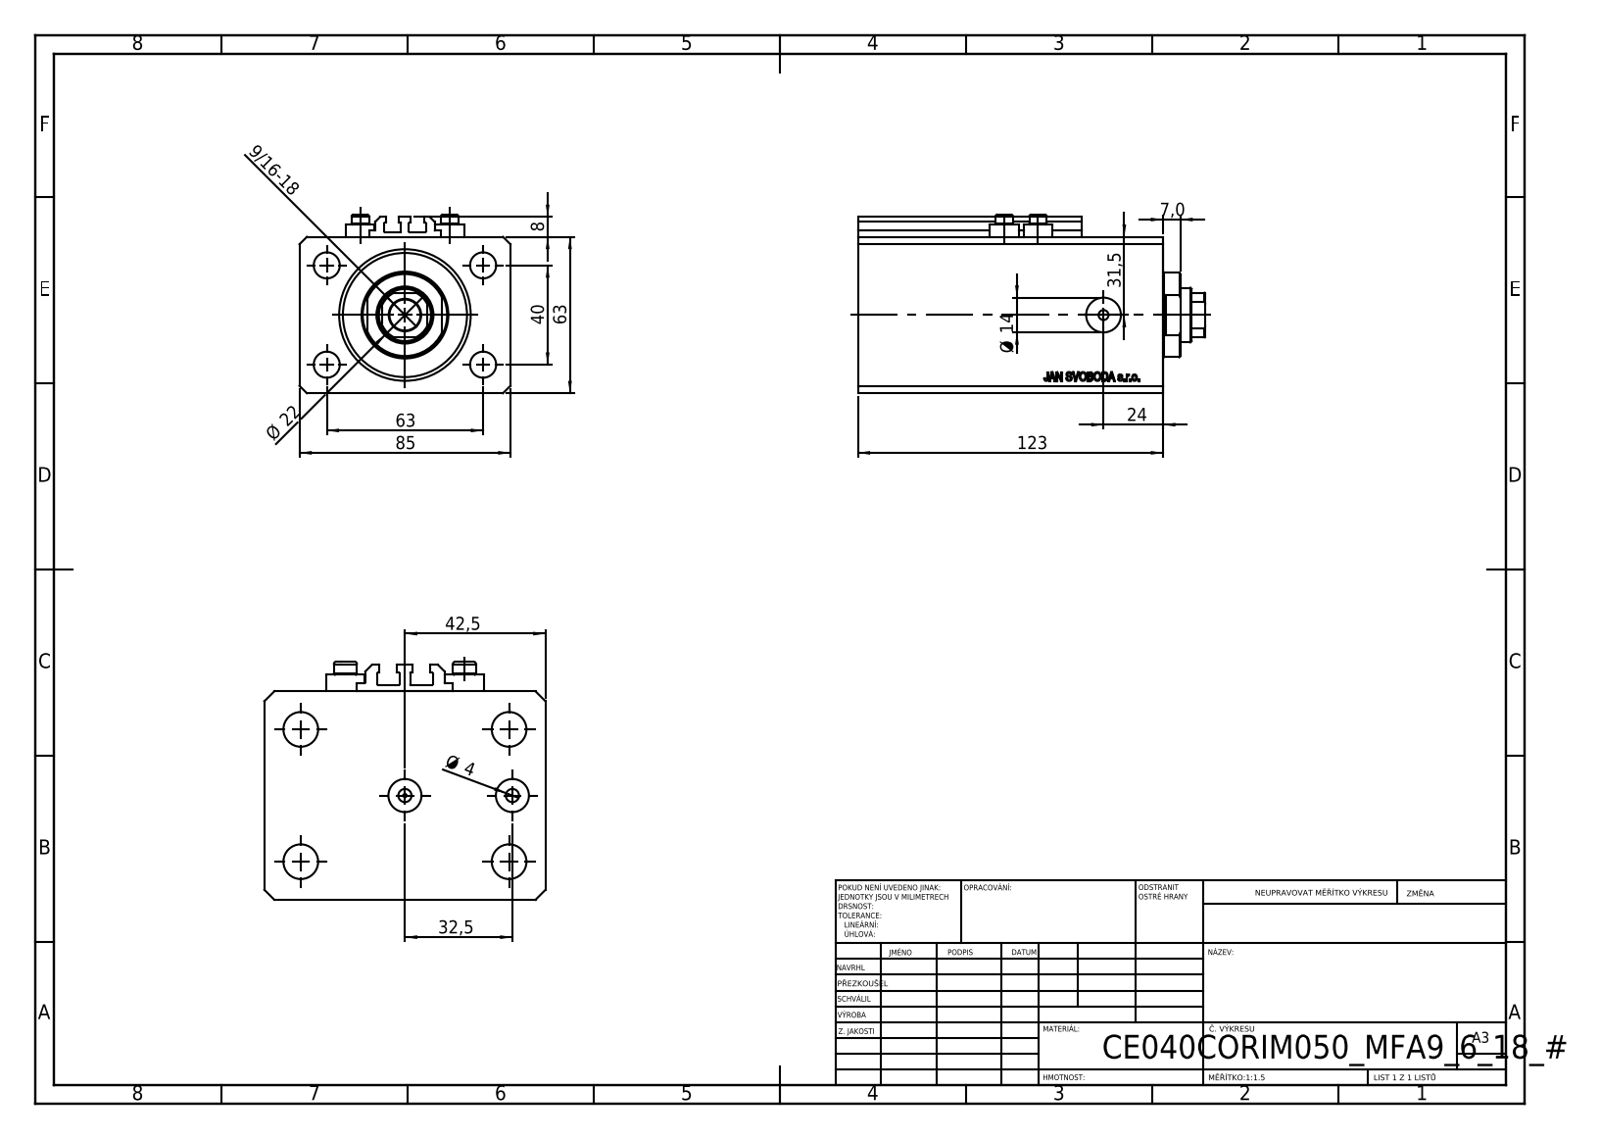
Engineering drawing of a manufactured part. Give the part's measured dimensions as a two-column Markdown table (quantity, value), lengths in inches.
| quantity | value |
| --- | --- |
| part name | V250CE_C_VCP; V250CE_C_Body; V250CE_VC_C; ALLEN BOLT V250CE |
| STEP written by | SolidWorks 2019 (CONFIG_CONTROL_DESIGN) |
| units | inches |
| bodies | 8 solids, 1038 faces (504 planar, 88 cylindrical, 446 other) |
| overall size | 5.512 × 3.346 × 2.835 |
| volume | 35.81 in³ |
| surface area | 177 in² |
| round holes (diameter × count) | 0.157 × 8, 0.413 × 4, 0.394 × 2, 0.551 × 2, 0.049 × 1, 0.492 × 1, 0.866 × 1, 1.575 × 1, 2.087 × 1 |
| round bosses / shafts (diameter × count) | 0.457 × 4, 0.276 × 4, 1.339 × 1 |
| partial cylindrical surfaces (radius × count) | 0.008 × 10, 0.413 × 1 |
| main face-to-face distances | 2.48, 3.346, 4.843, 0.669, 4.173, 0.449, 3.724, 4.394, 0.098, 0.394 |
| hole center spacings | 1.469, 0.535, 0.788, 1.417, 1.515, 1.575, 2.48, 2.64 |
